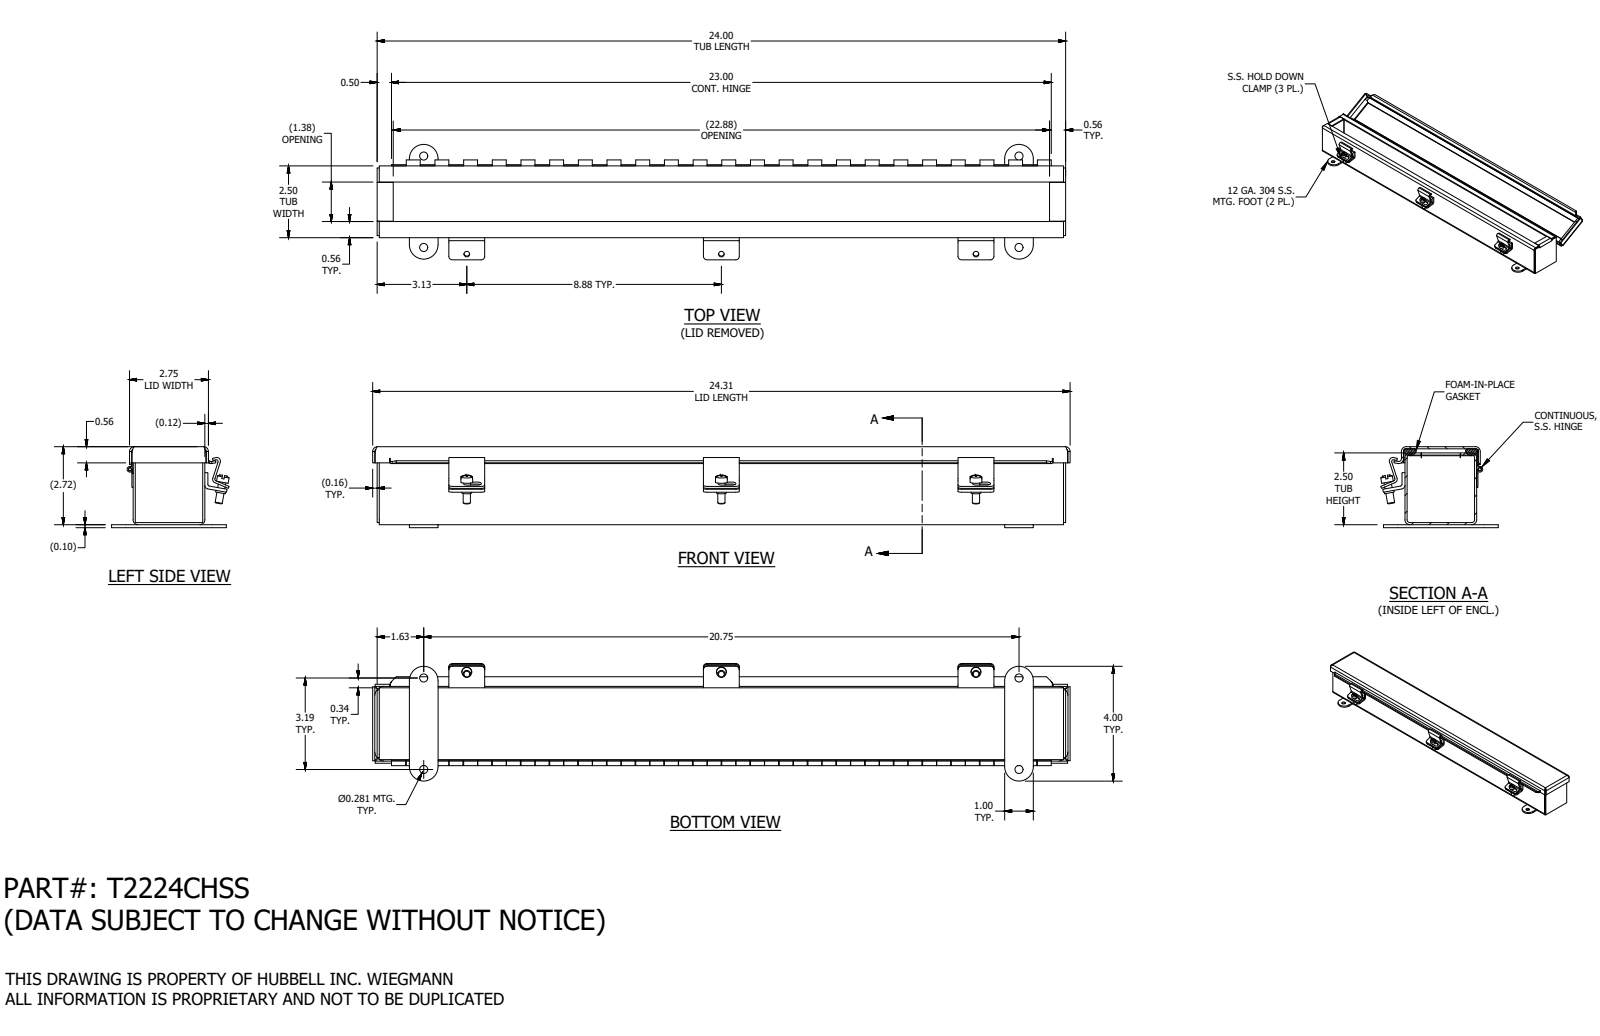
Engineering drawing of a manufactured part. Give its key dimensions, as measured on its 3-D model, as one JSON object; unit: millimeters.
{"part_name": "T2224CHSS", "step_written_by": "SolidWorks 2019 (AUTOMOTIVE_DESIGN)", "units": "millimeters", "bodies": {"solids": 19, "faces": 591, "planar": 355, "cylindrical": 197, "other": 39}, "overall_size": [617.6, 104.1, 71.7], "volume_mm3": 497000, "surface_area_mm2": 517100, "round_holes": [[2.8, 6], [7.1, 4], [5, 3], [2.9, 1]], "round_bosses_or_shafts": [[10.4, 3], [8.7, 3], [6.4, 3], [5.1, 1], [2.5, 1]], "partial_cylinders_radius": [[3.2, 12], [2.4, 11], [4.3, 11], [2.2, 8], [3.4, 6], [6.1, 4], [12.7, 4], [1.6, 3]], "face_to_face_distances": [1.9, 61.6, 67.2, 63.5, 59.7, 69, 65.3, 5.5, 64.8, 3.2], "hole_center_spacings": [225.4, 19.1, 80.9, 225.4, 450.9, 527.1, 533.2, 206.4]}
